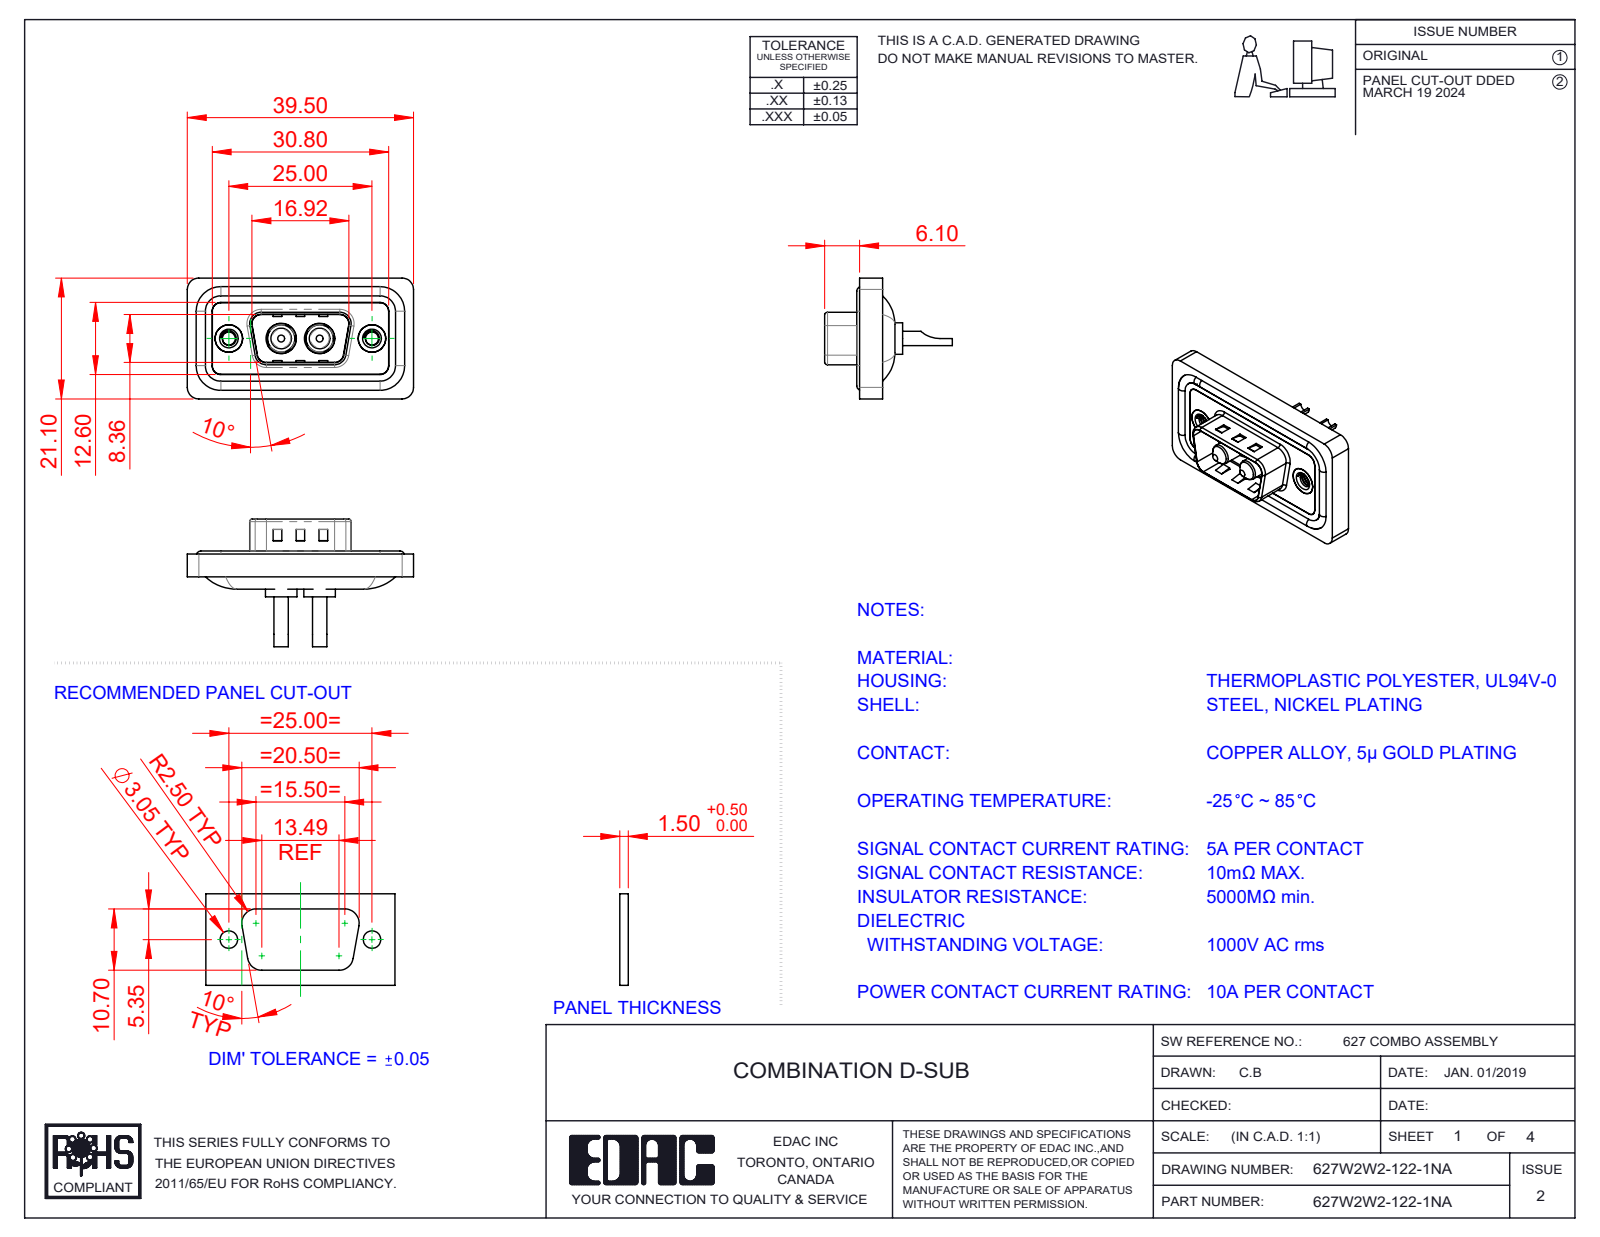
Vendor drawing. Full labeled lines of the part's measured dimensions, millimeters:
Part name (STEP PRODUCT): 627Combo Shell Front_09 Contacts; 627Combo Shell Rear_09 Contacts; Power Pin_10A SC; 627Combo Threaded Rivet_A (+3 more)
STEP written by: SolidWorks 2023 (CONFIG_CONTROL_DESIGN)
Units: millimetres
Bodies: 11 solids, 497 faces (169 planar, 226 cylindrical, 102 other)
Overall size (bounding box): 39.5 × 22.3 × 21.1
Volume: 4 457 mm³ · Surface area: 7 077 mm²
Round holes (diameter × count): ⌀1.7 ×2, ⌀2.26 ×2, ⌀4 ×2, ⌀4.8 ×2, ⌀4.85 ×2, ⌀5 ×2, ⌀5.3 ×2
Round bosses / shafts (diameter × count): ⌀1.6 ×4, ⌀5.5 ×2, ⌀5.2 ×2, ⌀4.9 ×2, ⌀4.75 ×2, ⌀3.75 ×2, ⌀3.6 ×2, ⌀2.5 ×2
Partial cylindrical surfaces — rounded edges, fillets, slot ends (radius × count): R1.5 ×22, R2 ×18, R0.5 ×8, R1.6 ×8, R0.25 ×4, R0.6 ×4, R0.65 ×4, R0.9 ×4
Main face-to-face distances: 0.4, 1.1, 2.9, 3.1, 0.5, 1.5, 1.6, 4, 2.5, 0.7
Hole centre spacings: 9.14, 15.86, 6.72, 25
